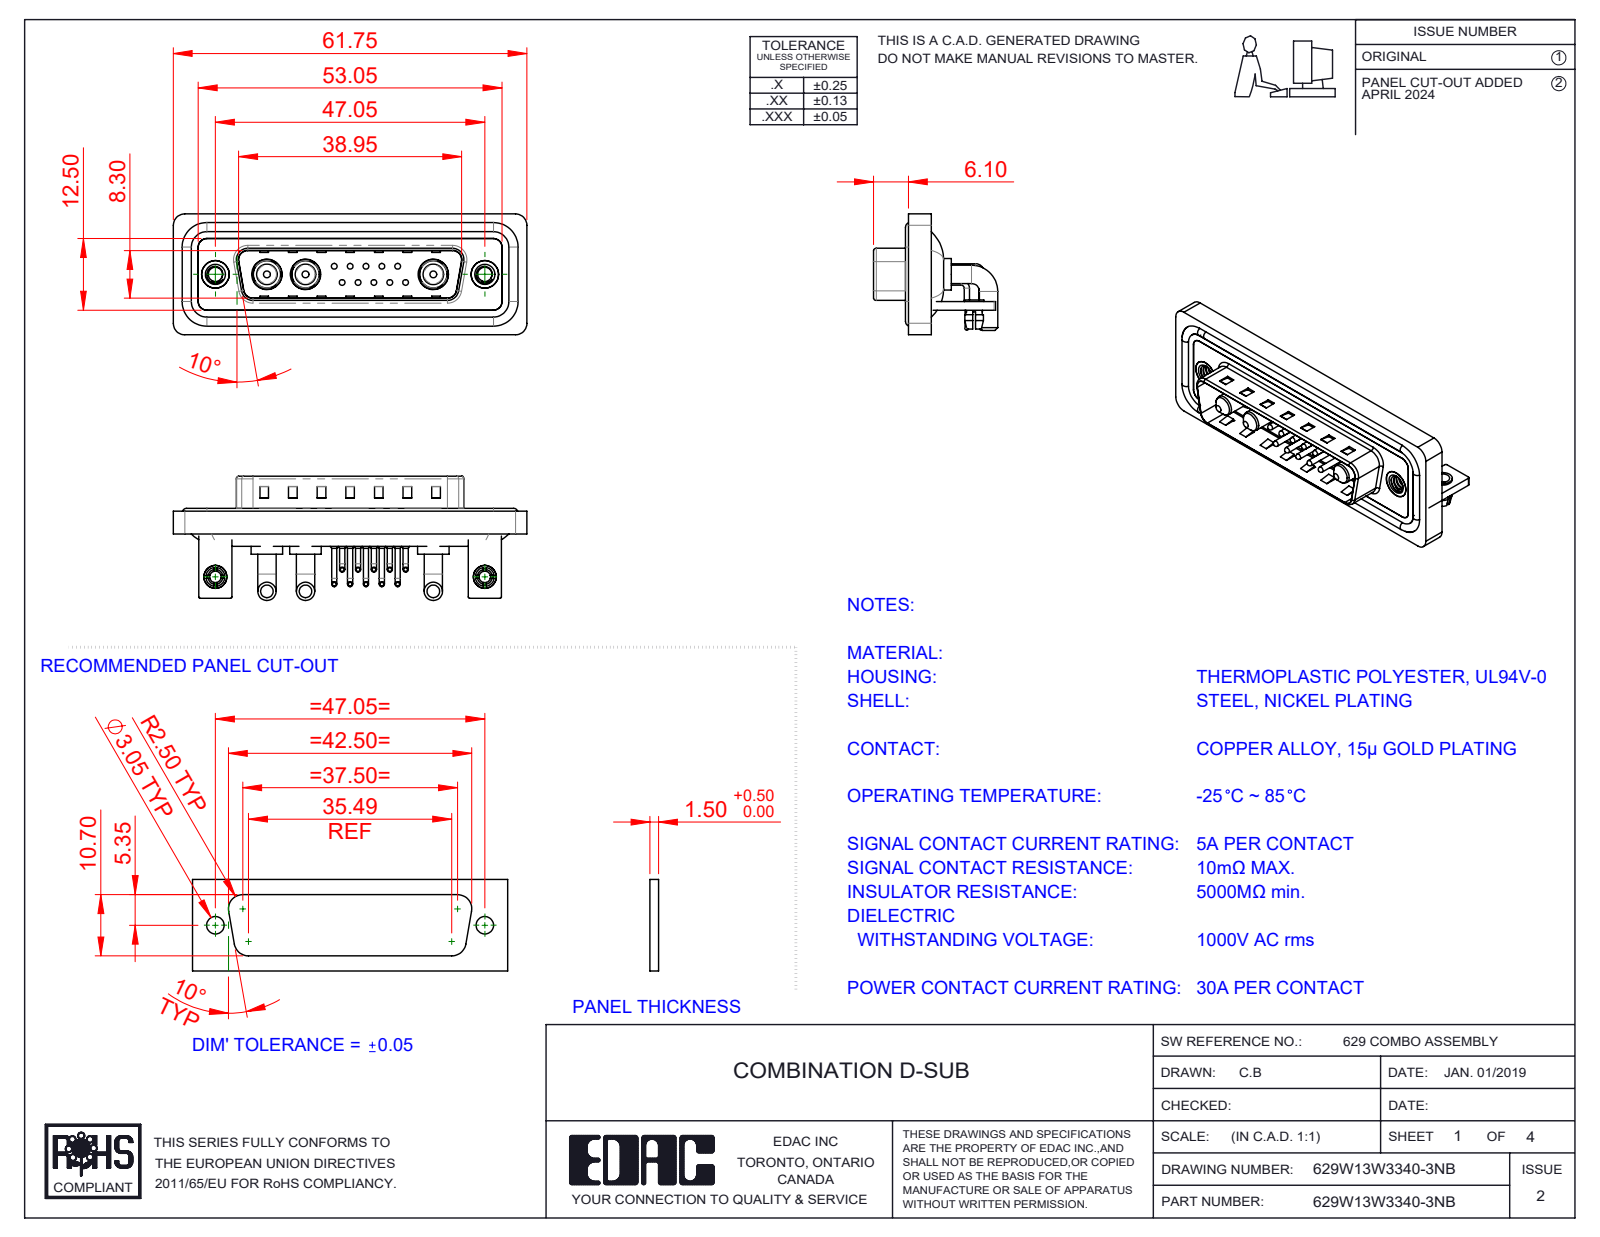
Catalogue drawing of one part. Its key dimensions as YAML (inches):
part_name: "629Combo Housing_13W3; 629Combo Board Lock; 629Combo Shell Front_25 Contacts; 629Combo Threaded Rivet_B (+7 more)"
step_written_by: "SolidWorks 2023 (CONFIG_CONTROL_DESIGN)"
units: inches
bodies: {solids: 27, faces: 1842, planar: 947, cylindrical: 661, other: 234}
overall_size: [2.431, 0.854, 0.831]
volume: 0.488
surface_area: 20.69
round_holes:
  - {diameter: 0.079, count: 12}
  - {diameter: 0.03, count: 10}
  - {diameter: 0.063, count: 10}
  - {diameter: 0.098, count: 4}
  - {diameter: 0.191, count: 3}
  - {diameter: 0.209, count: 3}
  - {diameter: 0.126, count: 2}
  - {diameter: 0.157, count: 2}
  - {diameter: 0.189, count: 2}
  - {diameter: 0.197, count: 2}
round_bosses_or_shafts:
  - {diameter: 0.035, count: 20}
  - {diameter: 0.059, count: 10}
  - {diameter: 0.039, count: 10}
  - {diameter: 0.026, count: 10}
  - {diameter: 0.126, count: 6}
  - {diameter: 0.063, count: 4}
  - {diameter: 0.217, count: 3}
  - {diameter: 0.205, count: 3}
partial_cylinders:
  - {radius: 0.079, count: 19}
  - {radius: 0.059, count: 18}
  - {radius: 0.01, count: 16}
  - {radius: 0.04, count: 10}
  - {radius: 0.02, count: 9}
  - {radius: 0.063, count: 8}
  - {radius: 0.024, count: 4}
  - {radius: 0.026, count: 4}
face_to_face_distances: [0.016, 0.031, 0.059, 0.114, 0.083, 0.043, 0.161, 0.063, 0.146, 0.177]
hole_center_spacings: [0.124, 0.109, 0.198, 0.218, 0.295, 0.198, 0.327, 0.398]
